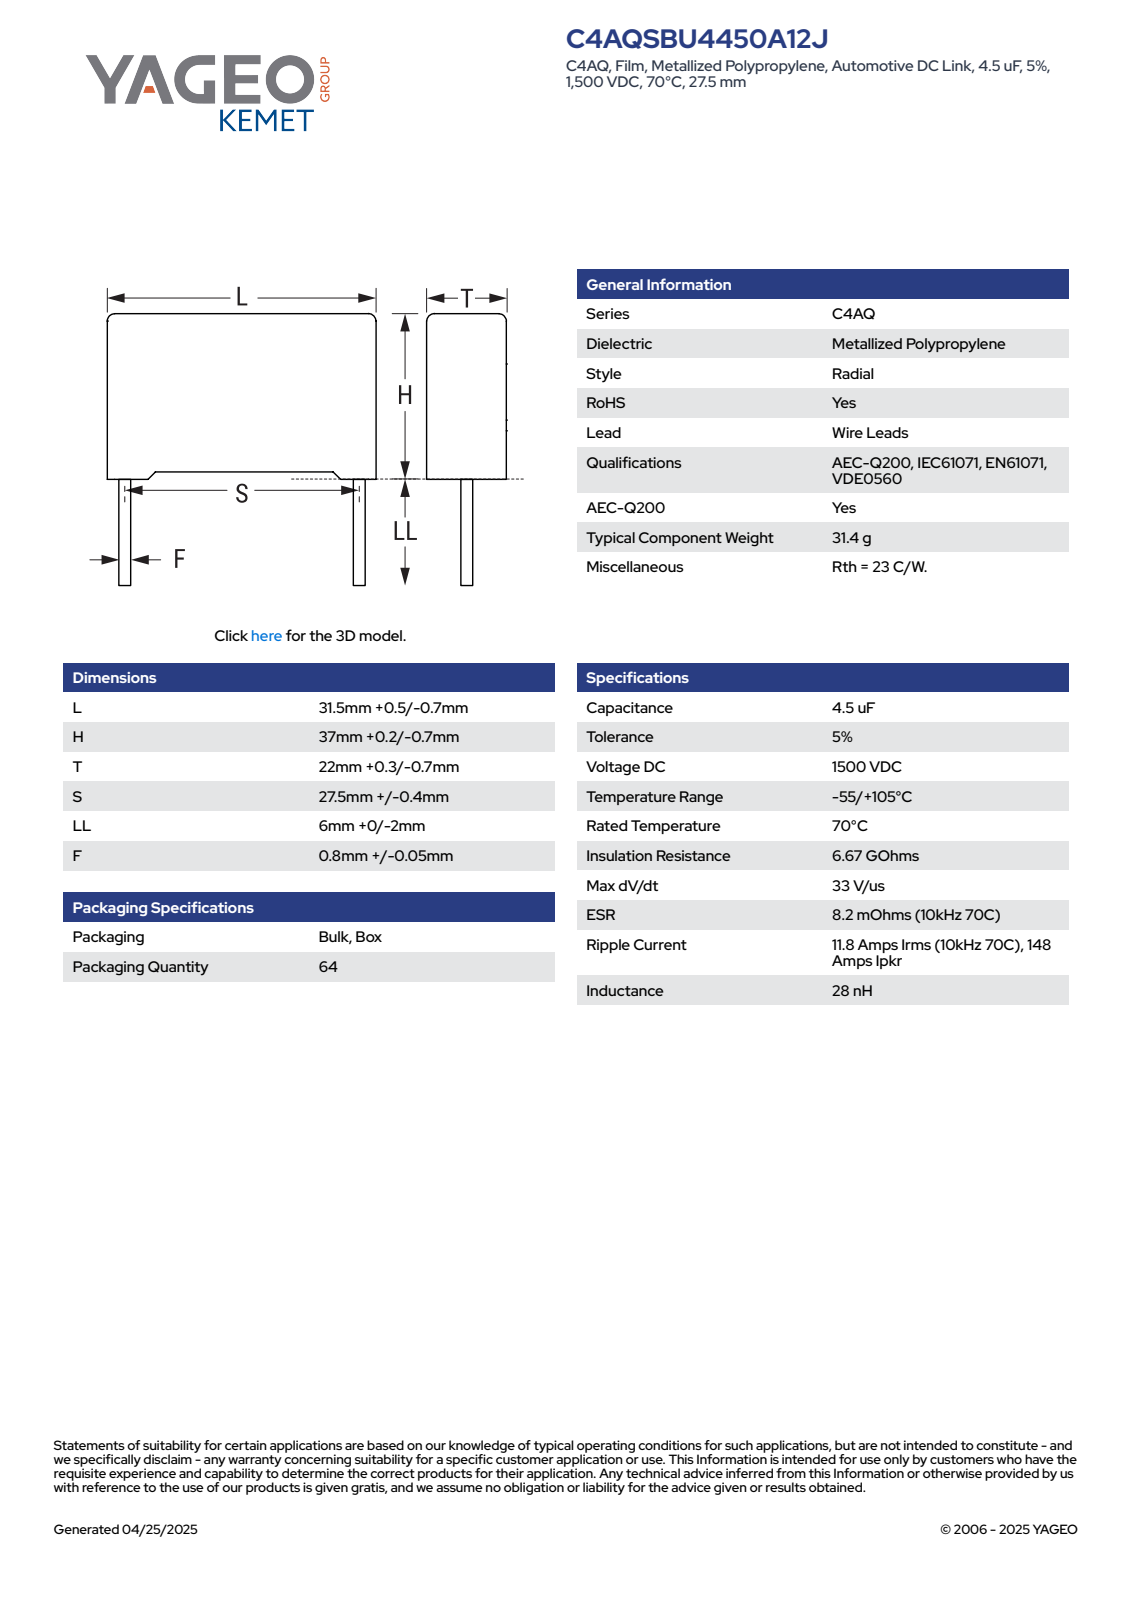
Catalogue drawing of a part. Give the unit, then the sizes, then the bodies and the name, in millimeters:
Units: millimetres
Overall size (bounding box): 43.2 × 32 × 22.3
Round bosses / shafts (diameter × count): ⌀0.85 ×2
Partial cylindrical surfaces — rounded edges, fillets, slot ends (radius × count): R0.5 ×4
Main face-to-face distances: 22.3, 32, 35.92, 0.53, 36.45, 0.75, 1.28, 37.2, 1.07, 30.93
Volume: 25 784 mm³ · Surface area: 5 549 mm²
Bodies: 4 solids, 85 faces (77 planar, 8 cylindrical, 0 other)
Part name (STEP PRODUCT): CFR_RB2CFP_31.5X37X22_L32H37.2T22.3S27.5LL6F0.85
STEP written by: SolidWorks 2014 (AUTOMOTIVE_DESIGN)
